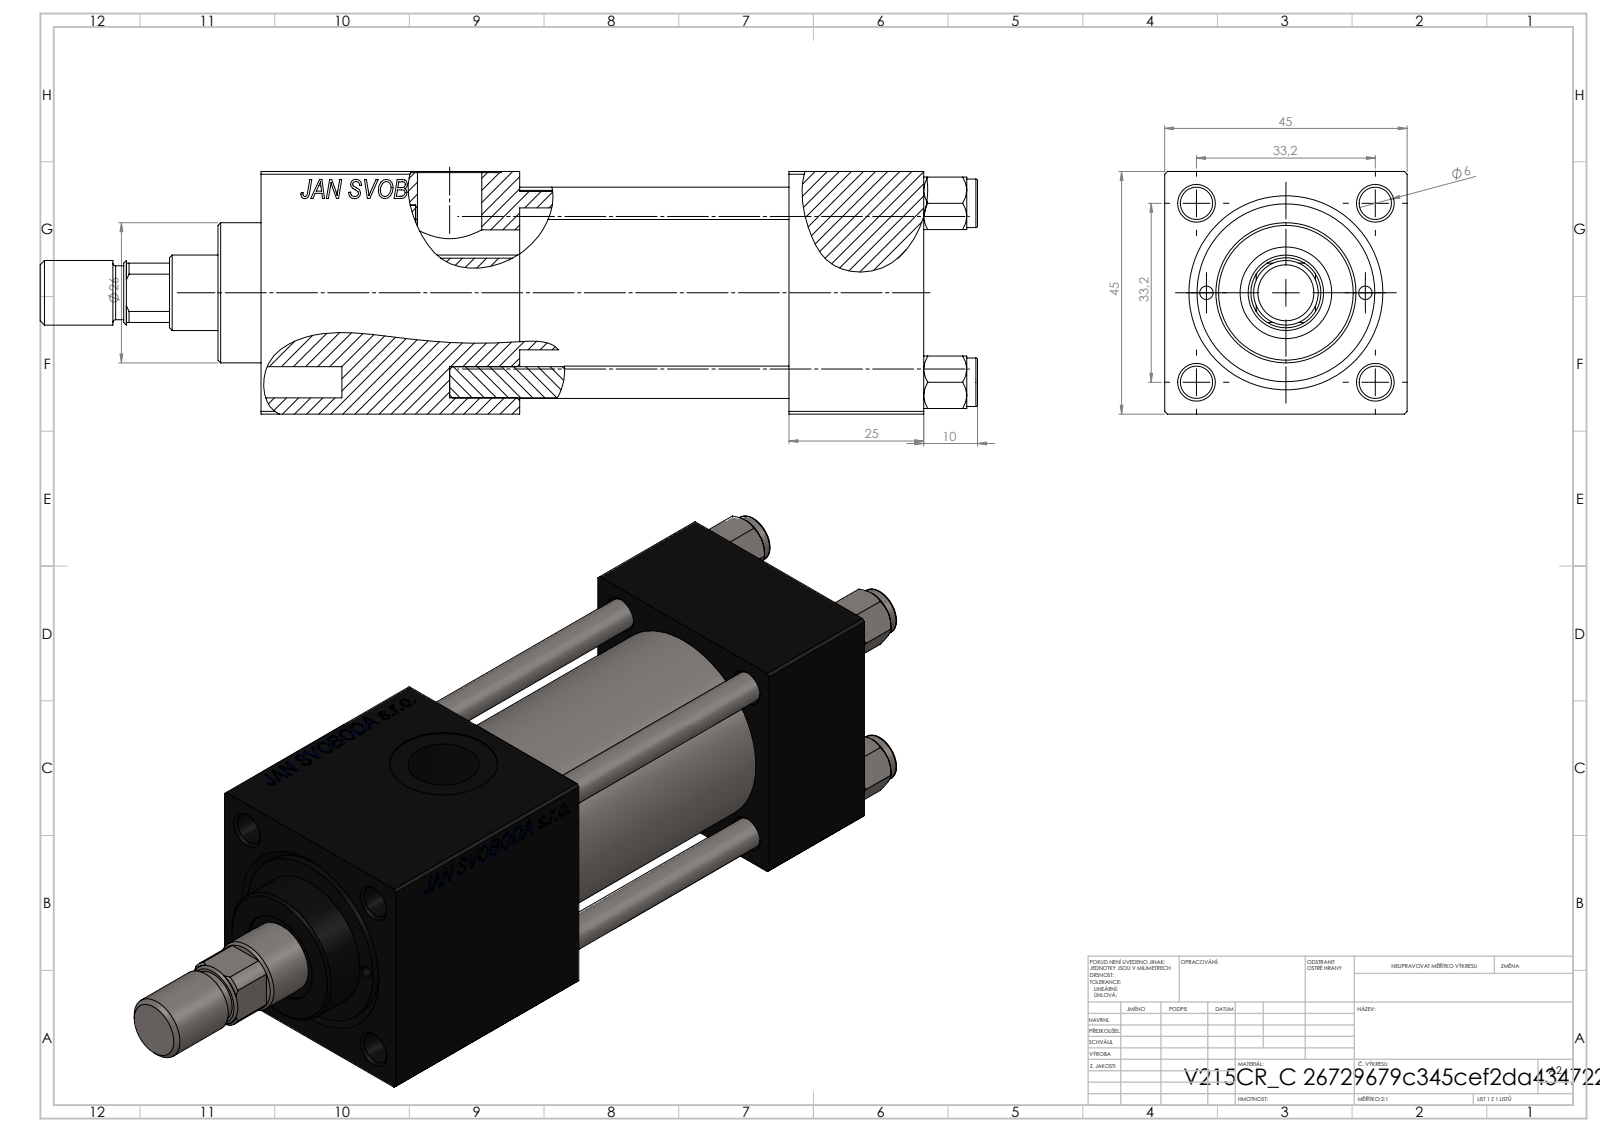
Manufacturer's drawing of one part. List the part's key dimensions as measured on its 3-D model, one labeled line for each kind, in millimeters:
Part name (STEP PRODUCT): V215_VC_A; ROD_END_AH; V215CR_C_TYCINKA; NUT_M5_C (+2 more)
STEP written by: SolidWorks 2019 (CONFIG_CONTROL_DESIGN)
Units: millimetres
Bodies: 12 solids, 1168 faces (531 planar, 95 cylindrical, 542 other)
Overall size (bounding box): 174 × 45 × 45
Volume: 195 503 mm³ · Surface area: 68 012 mm²
Round holes (diameter × count): ⌀6 ×4, ⌀2.5 ×2, ⌀7 ×2, ⌀13.16 ×2, ⌀20 ×2, ⌀6.5 ×1, ⌀14 ×1, ⌀17 ×1, ⌀24 ×1, ⌀32 ×1, ⌀33 ×1
Round bosses / shafts (diameter × count): ⌀9 ×4, ⌀38 ×1, ⌀26 ×1, ⌀12 ×1, ⌀10 ×1
Partial cylindrical surfaces — rounded edges, fillets, slot ends (radius × count): R6.5 ×1
Main face-to-face distances: 45, 25, 123, 98, 50, 75, 48, 94.3, 69.3, 19.3
Hole centre spacings: 16.7, 23.48, 33.2, 35.47, 14.75, 46.95, 29.5, 75.5
